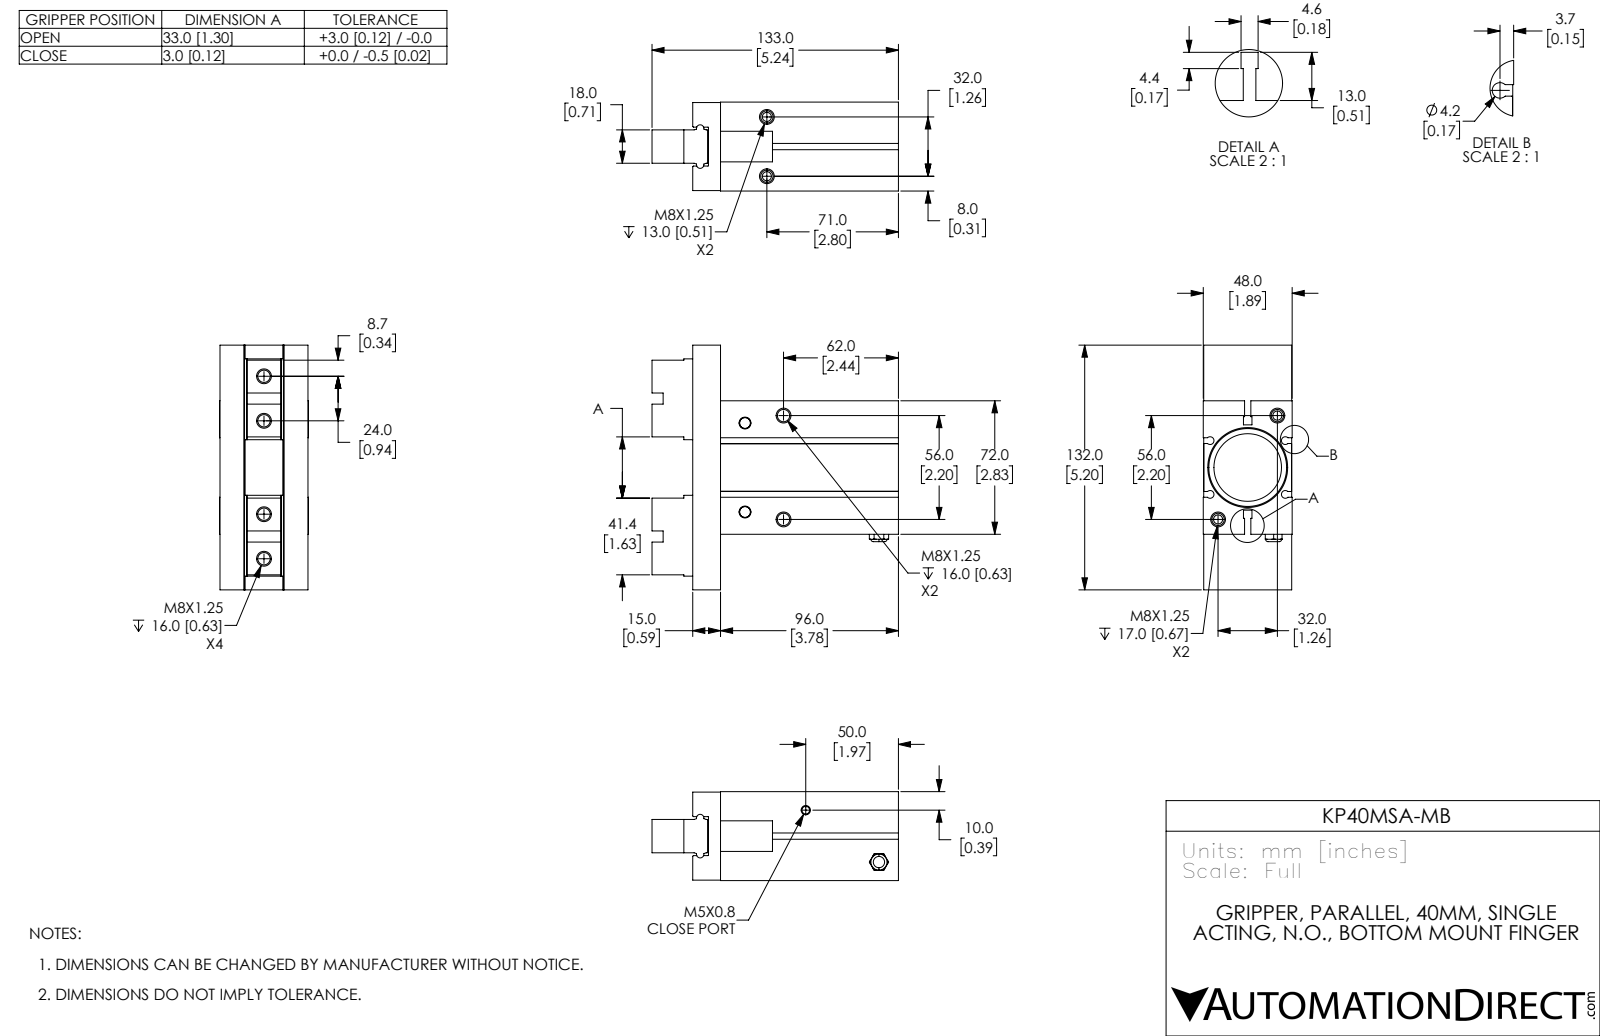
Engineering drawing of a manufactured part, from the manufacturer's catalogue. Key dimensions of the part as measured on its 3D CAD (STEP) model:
Part name (STEP PRODUCT): KP40MSA-MB; KP40MSA-MB-3; KP40MSA-MB-2; KP40MSA-MB-1
STEP written by: SolidWorks 2017 (CONFIG_CONTROL_DESIGN)
Units: millimetres
Bodies: 3 solids, 262 faces (135 planar, 65 cylindrical, 62 other)
Overall size (bounding box): 133 × 132 × 48
Volume: 384 779 mm³ · Surface area: 72 715 mm²
Round holes (diameter × count): ⌀6.65 ×8, ⌀0.5 ×2, ⌀4.13 ×2, ⌀6.65 ×2, ⌀8.02 ×2, ⌀6.1 ×1, ⌀36.5 ×1, ⌀42 ×1
Partial cylindrical surfaces — rounded edges, fillets, slot ends (radius × count): R0.2 ×7, R2.1 ×4, R0.3 ×2, R2 ×2
Main face-to-face distances: 15, 47.7, 33, 15.75, 32.25, 15.45, 31.95, 47.75, 15.5, 32
Hole centre spacings: 16.24, 24, 25.2, 26.56, 32.25, 49.2, 55.55, 74.4
